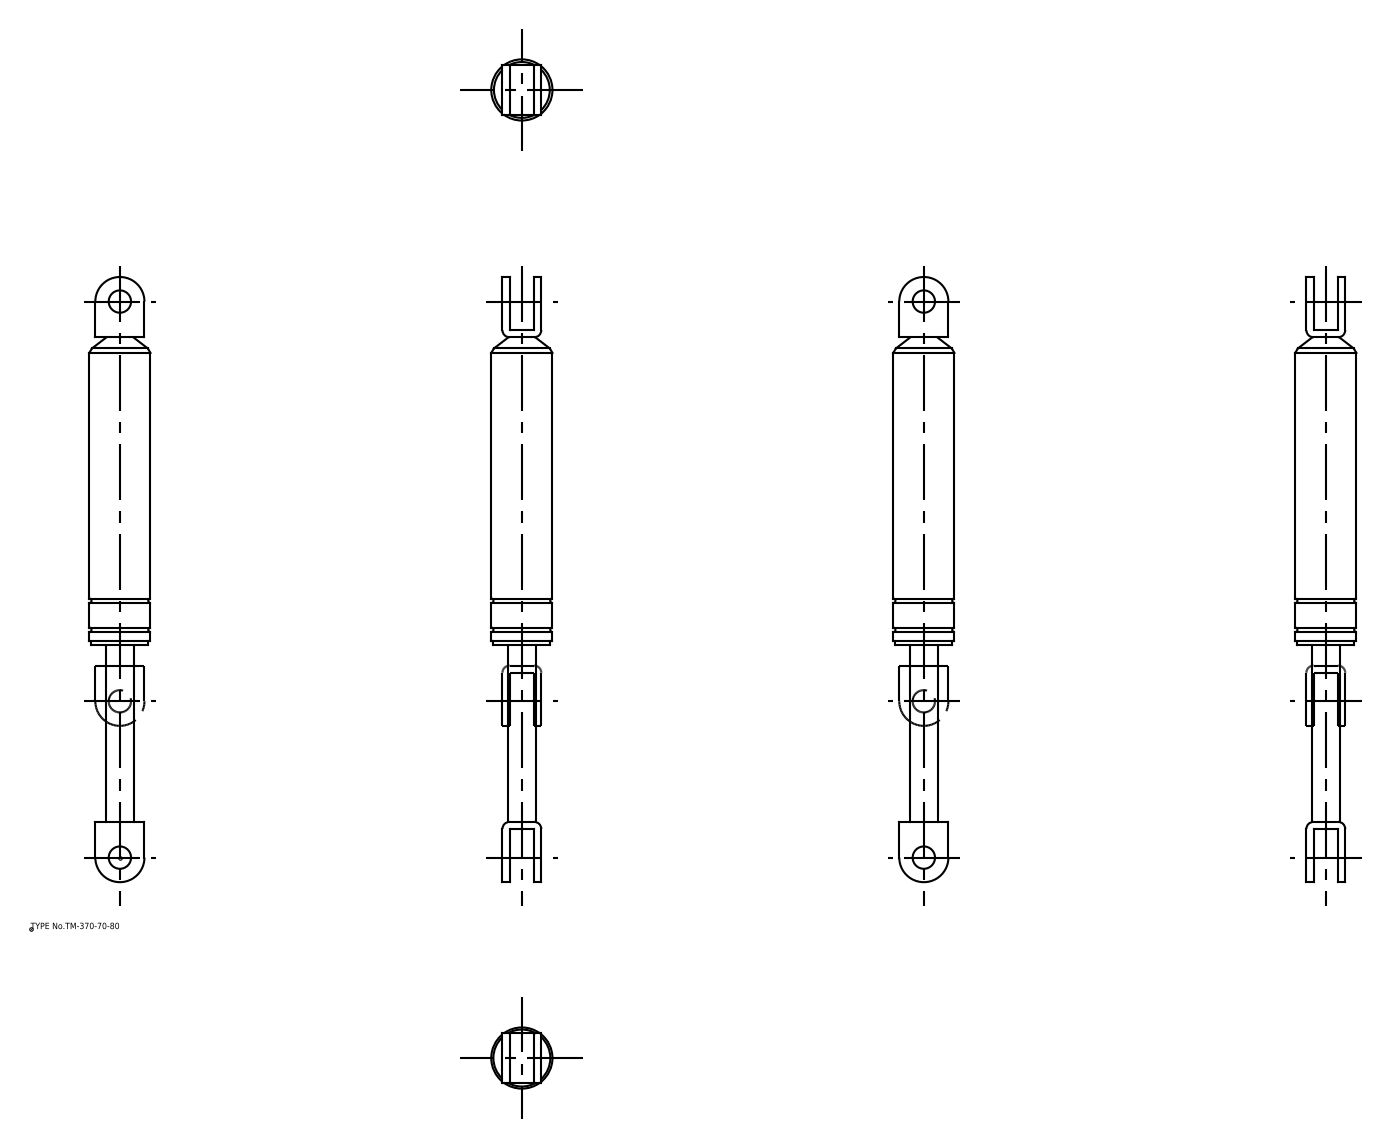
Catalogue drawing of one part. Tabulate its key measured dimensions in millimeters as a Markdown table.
| quantity | value |
| --- | --- |
| part name | TM_370_70_80; TM_370_70_80_div |
| STEP written by | spGate 16.7.1 (AUTOMOTIVE_DESIGN) |
| units | millimeters |
| bodies | 2 solids, 64 faces (22 planar, 32 cylindrical, 10 other) |
| overall size | 271 × 28.2 × 28.2 |
| volume | 96 750 mm³ |
| surface area | 21 763 mm² |
| round holes (diameter × count) | 10 × 2 |
| round bosses / shafts (diameter × count) | 28.2 × 1, 27.4 × 1, 25.5 × 1, 12.5 × 1 |
| partial cylindrical surfaces (radius × count) | 3.2 × 4, 11 × 2 |
| main face-to-face distances | 3.2, 14.2, 17.4, 11, 22, 220.2, 82.2, 223.4, 141.2, 138 |
| hole center spacings | 249 |
